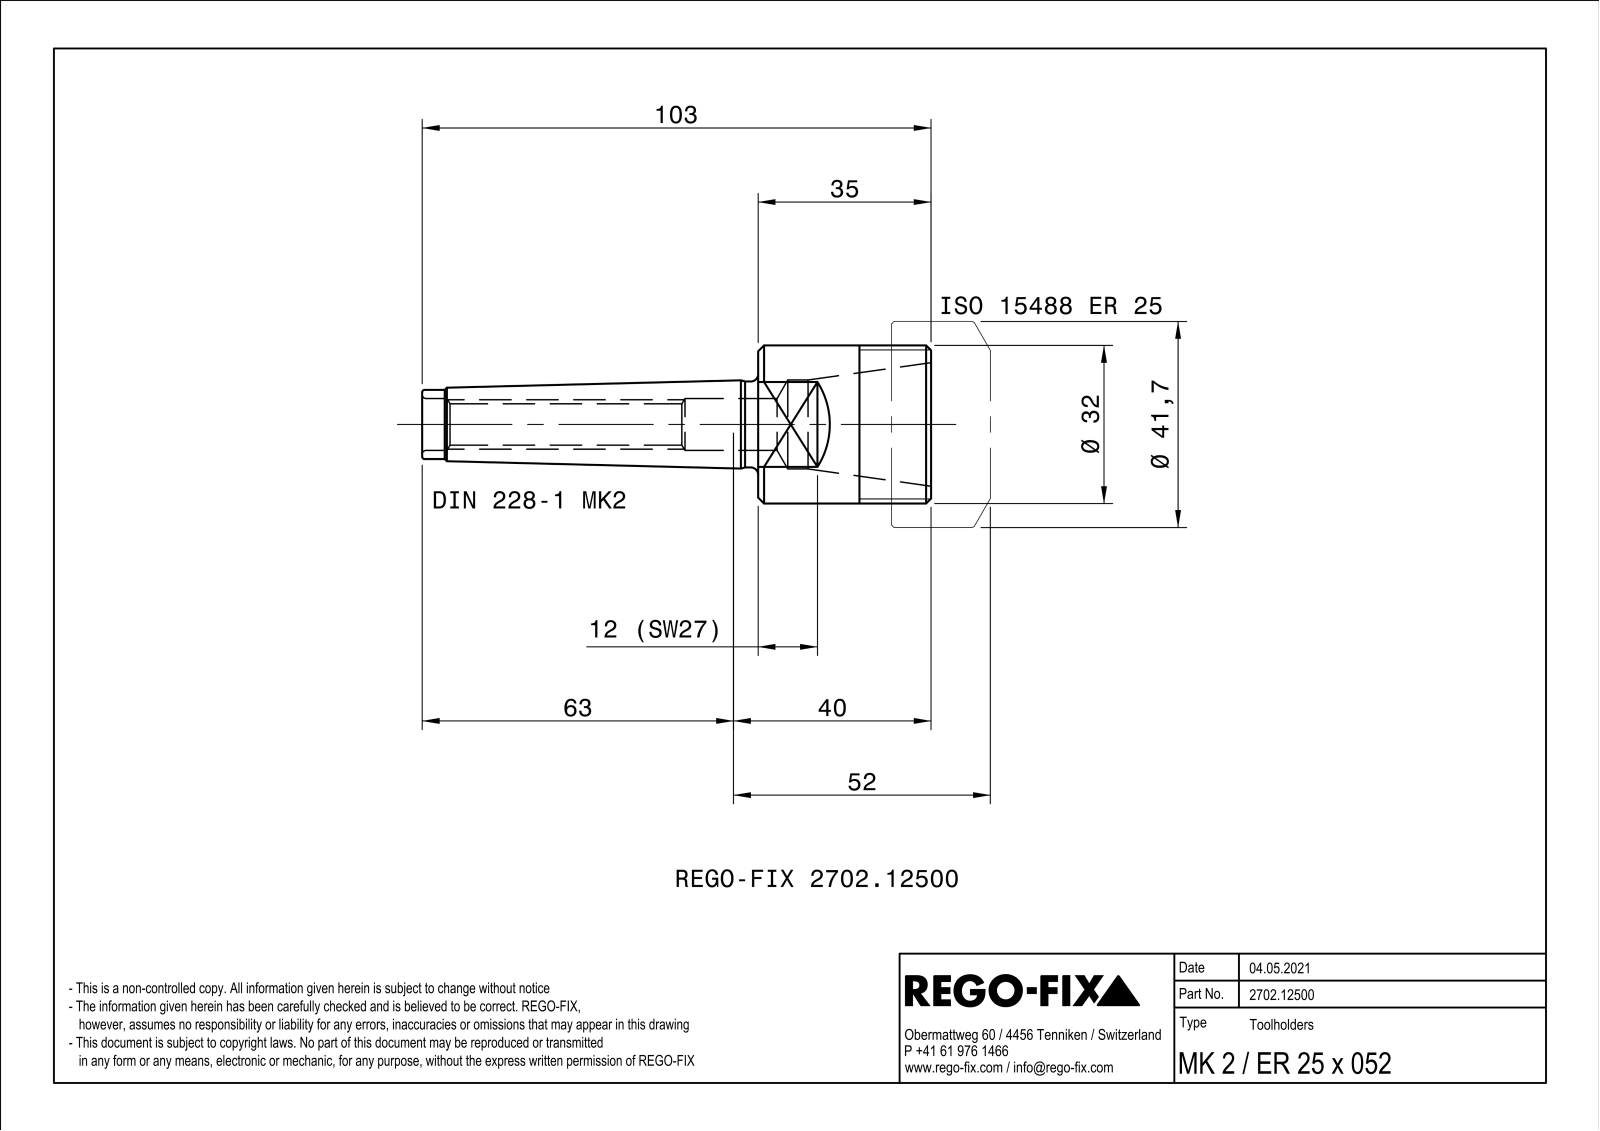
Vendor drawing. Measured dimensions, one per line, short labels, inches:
name: NOCUT
written by: SIEMENS PLM Software Solid Edge ST10 (AUTOMOTIVE_DESIGN)
unit: in
bodies: 1 solid, 32 faces (9 planar, 9 cylindrical, 14 other)
size: 4.055 × 1.26 × 1.26
volume: 1.6 in³; area: 18.45 in²
holes: 1× ⌀0.33, 1× ⌀0.413, 1× ⌀0.709
bosses: 1× ⌀1.26, 1× ⌀0.685, 1× ⌀0.551
face distances: 1.378, 1.063, 0.306, 4.055, 2.677
